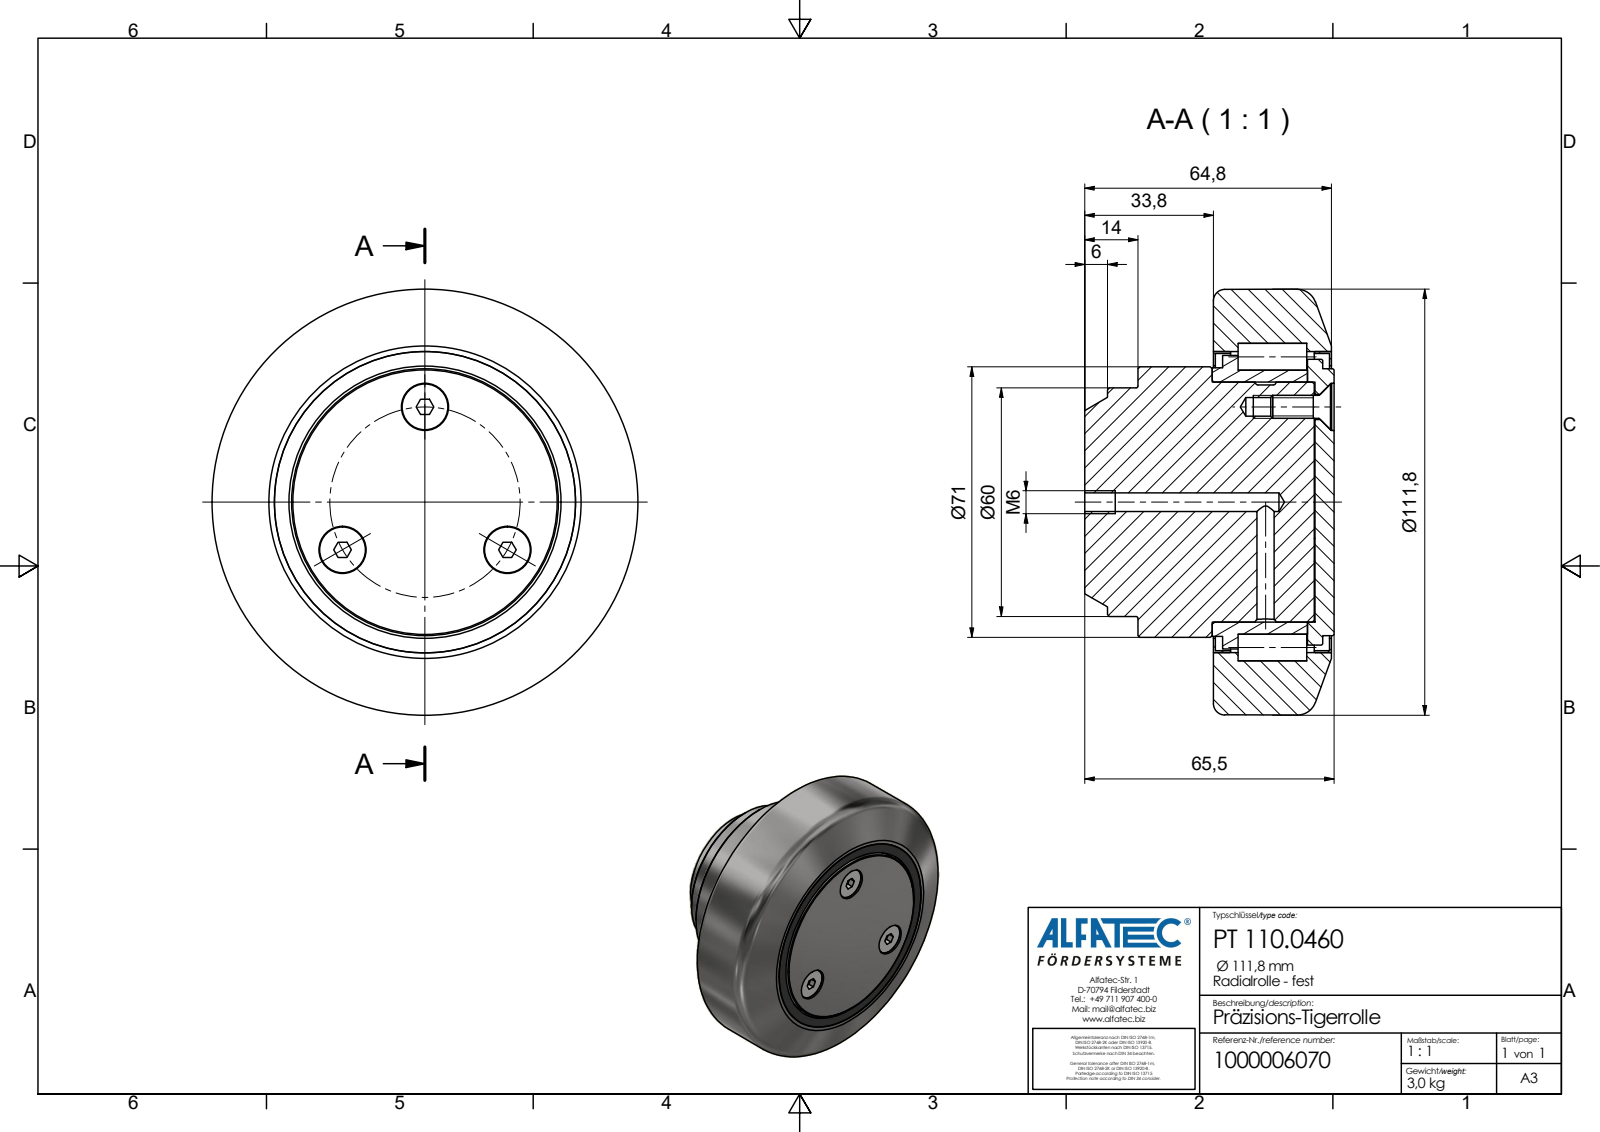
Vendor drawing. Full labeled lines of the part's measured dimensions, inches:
Part name (STEP PRODUCT): PT110.0460_Kontur
STEP written by: Autodesk Inventor 2020 (AP242_MANAGED_MODEL_BASED_3D_ENGINEERING_MIM_LF)
Units: inches
Bodies: 2 solids, 86 faces (41 planar, 26 cylindrical, 19 other)
Overall size (bounding box): 4.402 × 4.402 × 2.579
Volume: 22.39 in³ · Surface area: 91.3 in²
Round holes (diameter × count): ⌀0.488 ×3, ⌀0.118 ×1, ⌀0.177 ×1, ⌀0.194 ×1, ⌀2.48 ×1, ⌀2.815 ×1, ⌀3.071 ×1, ⌀3.11 ×1, ⌀3.28 ×1
Round bosses / shafts (diameter × count): ⌀0.472 ×3, ⌀3.031 ×1, ⌀2.953 ×1, ⌀2.795 ×1, ⌀2.776 ×1, ⌀2.756 ×1, ⌀2.728 ×1, ⌀2.421 ×1
Main face-to-face distances: 1.248, 0.256, 0.965, 1.331, 2.579, 0.236, 0.02, 1.201, 1.587, 0.992
Hole centre spacings: 0.984, 1.705
